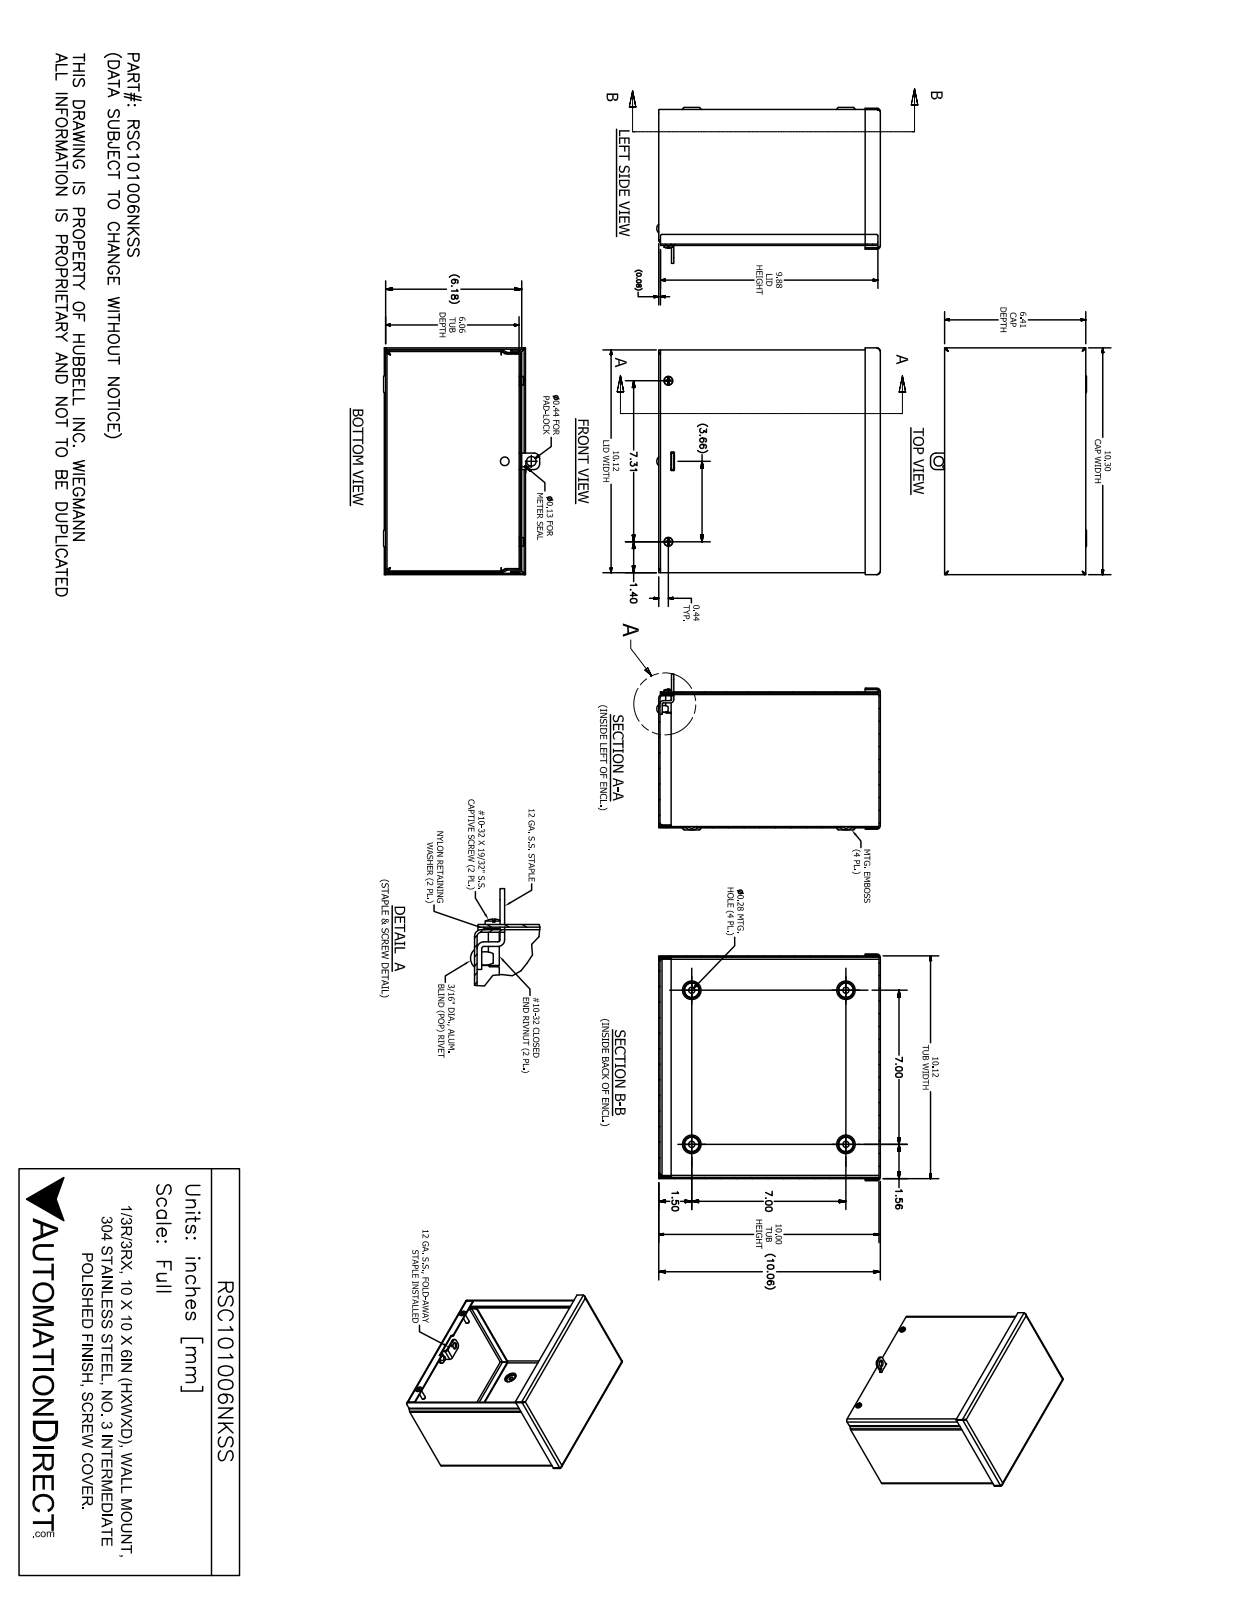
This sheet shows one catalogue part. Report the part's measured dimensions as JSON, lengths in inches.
{"part_name": "RSC101006NKSS", "step_written_by": "SolidWorks 2017 (AUTOMOTIVE_DESIGN)", "units": "inches", "bodies": {"solids": 12, "faces": 369, "planar": 191, "cylindrical": 93, "other": 85}, "overall_size": [10.299, 10.149, 7.084], "volume_in3": 29.03, "surface_area_in2": 994.3, "round_holes": [[0.25, 4], [0.281, 4], [0.156, 2], [0.196, 2], [0.257, 2], [0.278, 2], [0.125, 1], [0.198, 1], [0.201, 1], [0.437, 1]], "round_bosses_or_shafts": [[0.453, 2], [0.406, 2], [0.248, 2], [0.167, 2], [0.187, 1]], "partial_cylinders_radius": [[0.094, 16], [0.153, 16], [0.031, 6], [0.25, 4], [0.047, 2], [0.05, 2], [0.062, 2], [0.089, 2]], "face_to_face_distances": [0.059, 6.117, 10, 10.059, 6.176, 6.058, 9.941, 10.118, 0.117, 0.059], "hole_center_spacings": [7, 1.074, 1.105, 7.235, 7.239, 7.313, 8.064, 8.095]}
